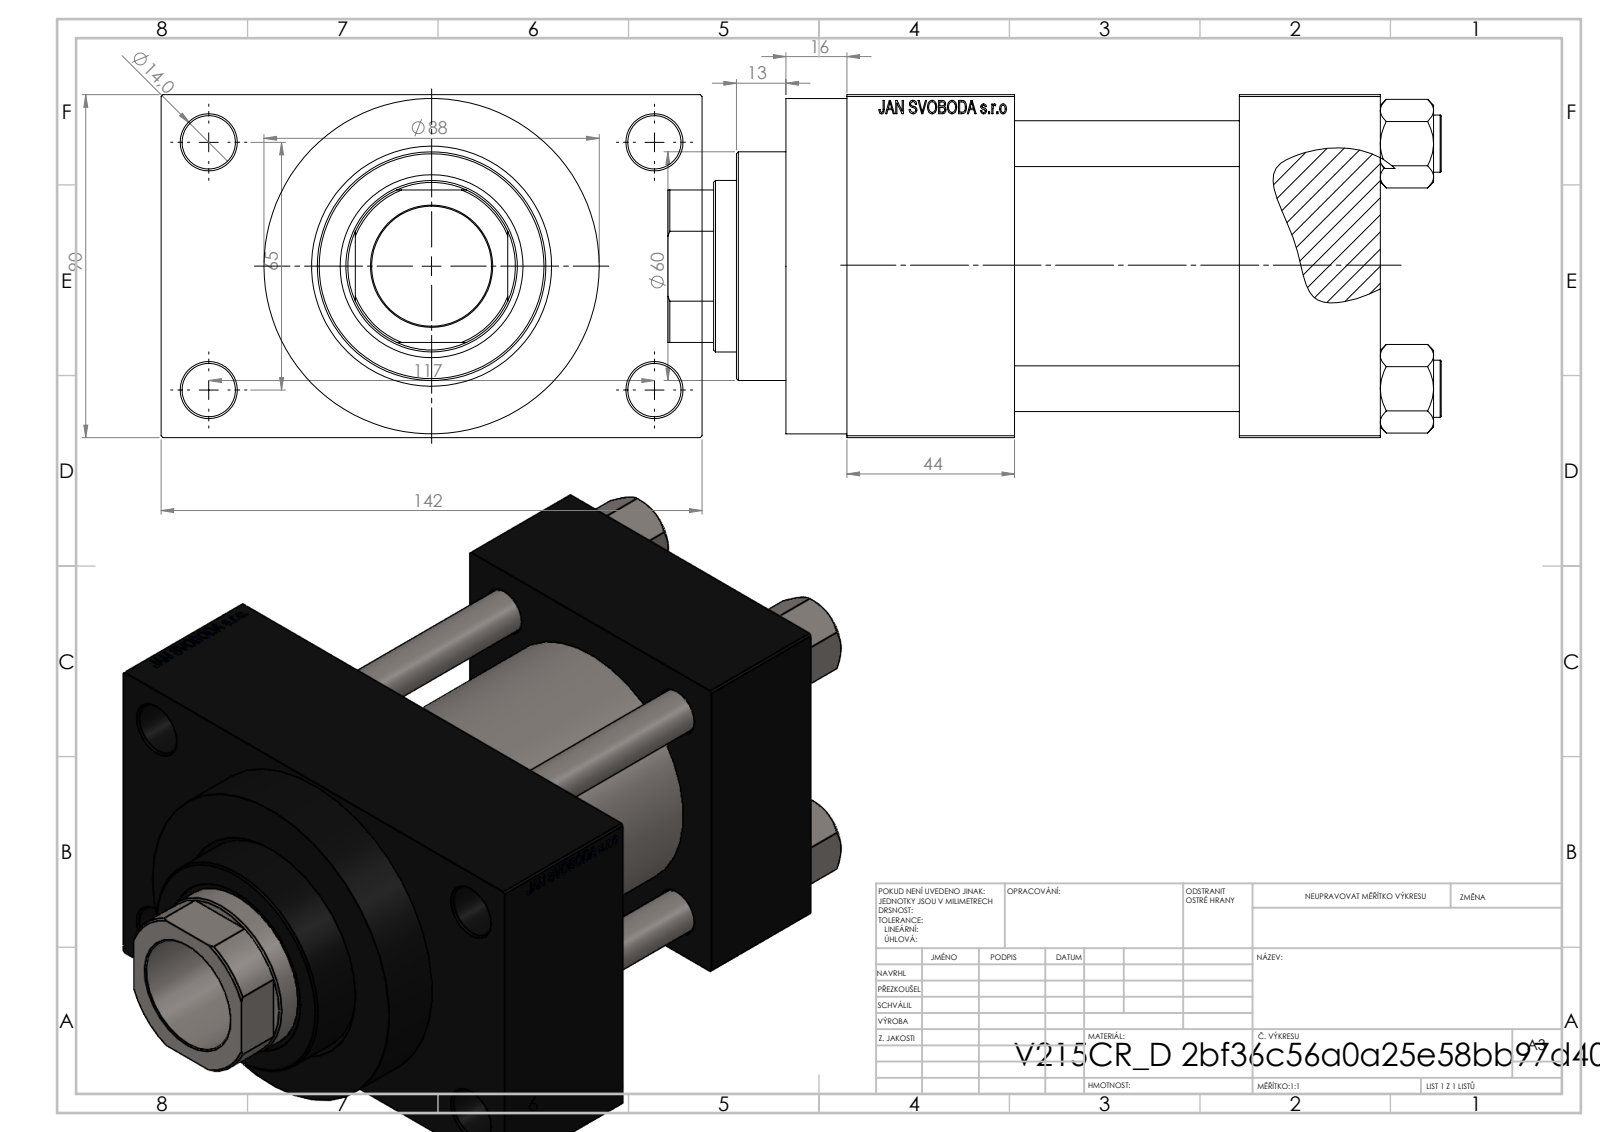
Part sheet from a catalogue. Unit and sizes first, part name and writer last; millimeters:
Units: millimetres
Overall size (bounding box): 203 × 142 × 90
Round holes (diameter × count): ⌀12 ×4, ⌀14 ×4, ⌀7 ×2, ⌀20.96 ×2, ⌀30 ×2, ⌀31.5 ×1, ⌀45 ×1, ⌀48 ×1, ⌀50 ×1, ⌀60 ×1, ⌀63 ×1
Round bosses / shafts (diameter × count): ⌀15 ×4, ⌀88 ×1, ⌀69 ×1
Partial cylindrical surfaces — rounded edges, fillets, slot ends (radius × count): R22 ×1
Main face-to-face distances: 90, 59, 37, 96, 26, 140, 103, 44, 116, 60
Hole centre spacings: 26.35, 45.47, 64.3, 66.92, 69.81, 90.65, 111.34, 65
Volume: 1 160 000 mm³ · Surface area: 212 384 mm²
Bodies: 11 solids, 1102 faces (496 planar, 86 cylindrical, 520 other)
Part name (STEP PRODUCT): V215CR_VCP_D; V215CR_D_Body; V215_VC_A; V215CR_D_TYCINKA (+1 more)
STEP written by: SolidWorks 2019 (CONFIG_CONTROL_DESIGN)
